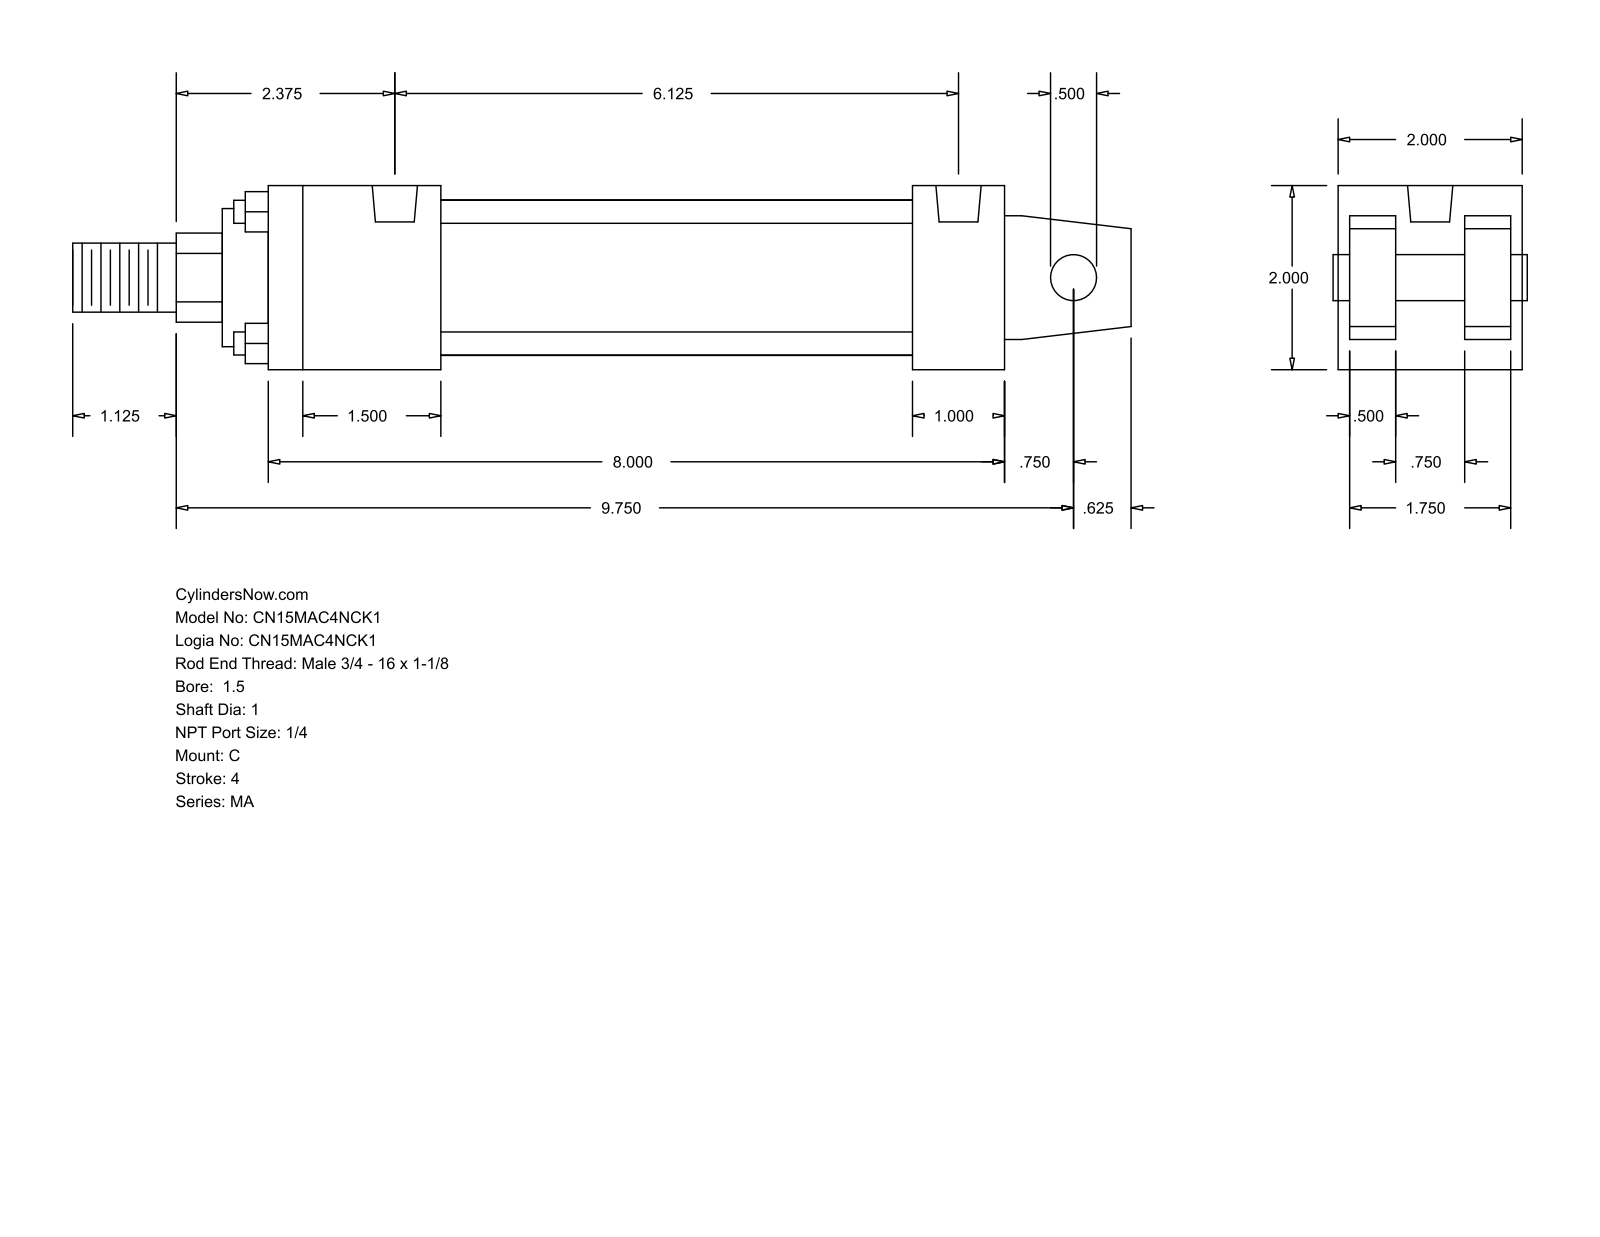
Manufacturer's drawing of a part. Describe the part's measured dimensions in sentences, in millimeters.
The part is named "MA_C__0150_1". Its 3-D file was written by "GSSL Pune (CONFIG_CONTROL_DESIGN)". It is 0 solids with 103 faces: 76 planar, 27 cylindrical and 0 other. Overall it measures 292.1 by 50.8 by 50.8 millimeters. Round holes: 4 of diameter 7.94, 2 of diameter 12.49. Round bosses or shafts: 4 of diameter 6.35, 1 of diameter 42.93, 1 of diameter 38.1, 1 of diameter 25.4, 1 of diameter 19.05, 1 of diameter 12.7. Partial cylindrical surfaces (rounded edges, fillets, slot ends): 1 of radius 12.29. The main face-to-face distances are 50.8, 47.63, 12.7, 3.17, 15.87, 34.93, 31.76, 203.2, 25.4, 177.8. The hole center spacings are 155.57.
